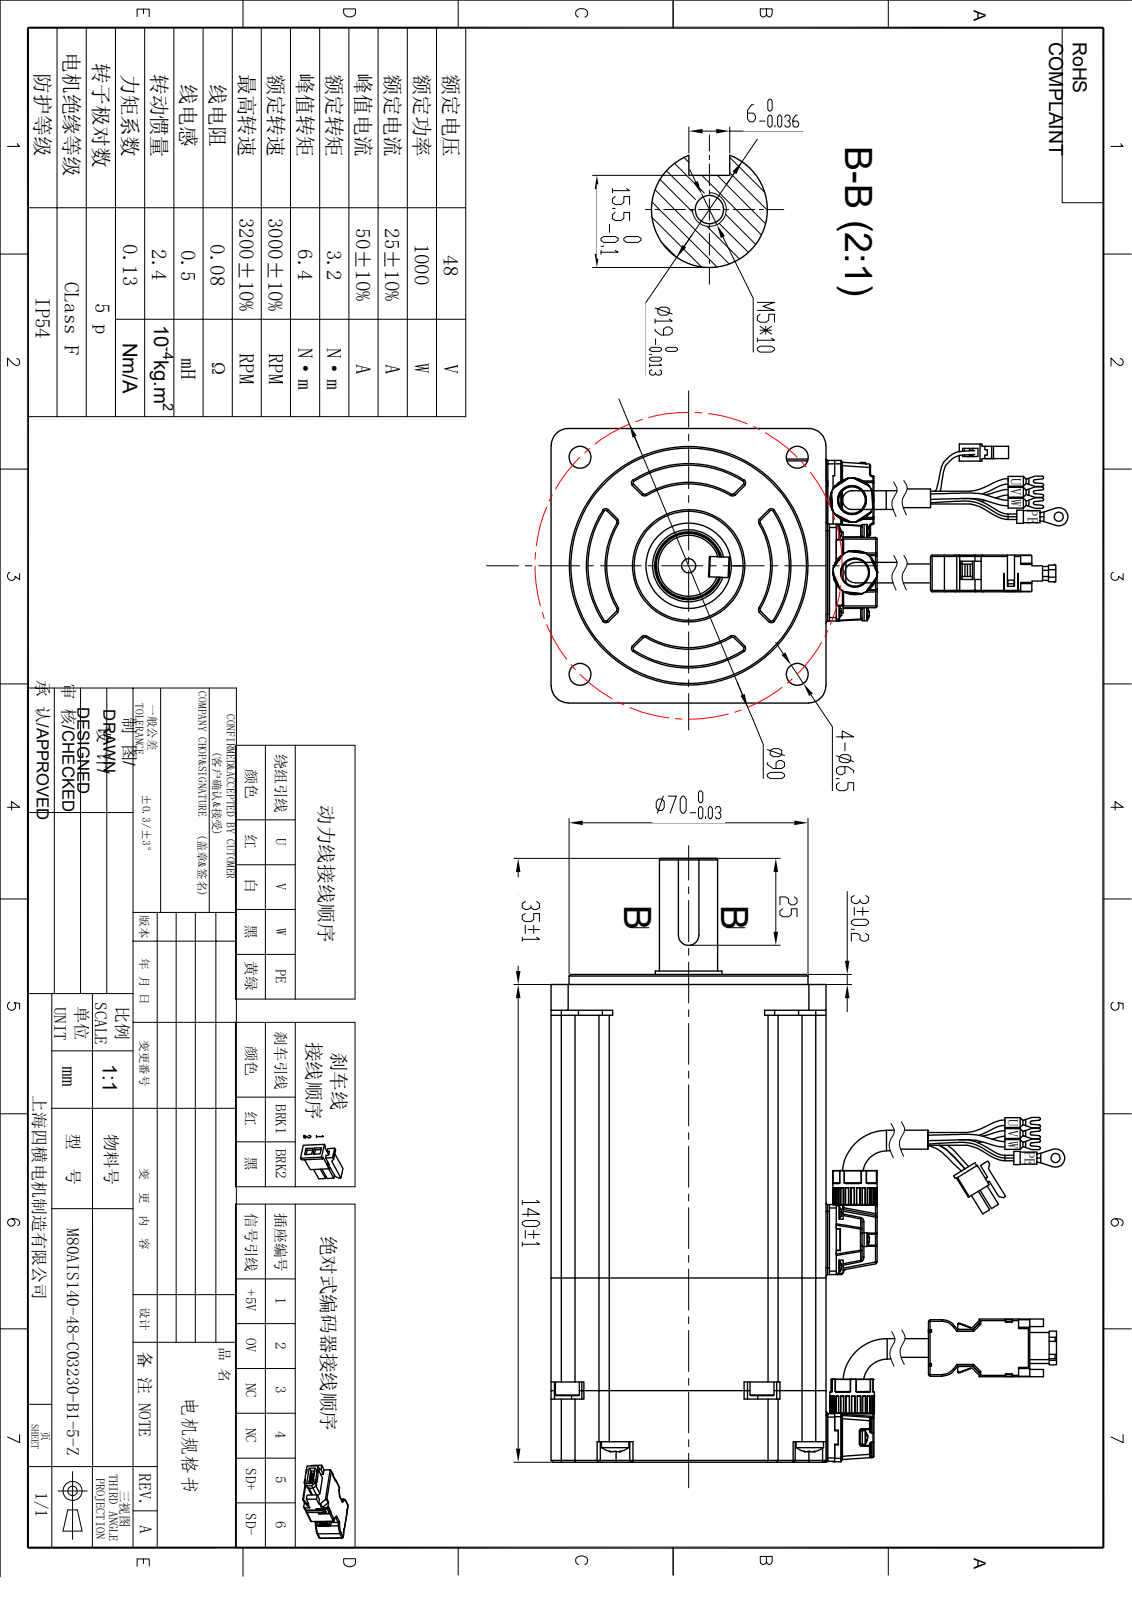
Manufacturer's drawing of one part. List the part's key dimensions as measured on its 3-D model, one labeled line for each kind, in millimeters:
Part name (STEP PRODUCT): M80AIS140-48-C03230-B1-5-Z
STEP written by: SolidWorks 2020 (CONFIG_CONTROL_DESIGN)
Units: millimetres
Bodies: 0 solids, 2036 faces (889 planar, 737 cylindrical, 410 other)
Overall size (bounding box): 175.2 × 95.5 × 80.5
Round holes (diameter × count): ⌀3.3 ×11, ⌀1.6 ×9, ⌀4.2 ×9, ⌀2.2 ×8, ⌀2.05 ×4, ⌀6.5 ×4, ⌀2.5 ×3, ⌀8.5 ×2, ⌀7.8 ×1, ⌀8 ×1, ⌀18 ×1, ⌀25 ×1
Round bosses / shafts (diameter × count): ⌀4 ×20, ⌀1 ×9, ⌀2 ×8, ⌀1.73 ×8, ⌀8 ×5, ⌀7 ×4, ⌀3.46 ×4, ⌀13 ×2
Partial cylindrical surfaces — rounded edges, fillets, slot ends (radius × count): R0.5 ×87, R1 ×60, R0.1 ×48, R0.3 ×41, R0.38 ×24, R0.61 ×24, R3 ×24, R0.2 ×19
Main face-to-face distances: 80.5, 2, 14, 66.5, 138.2, 19, 6, 3, 21, 140.2
Hole centre spacings: 10.96, 41.5, 53.45, 58.69, 68.11, 85.88, 4.5, 7.92
